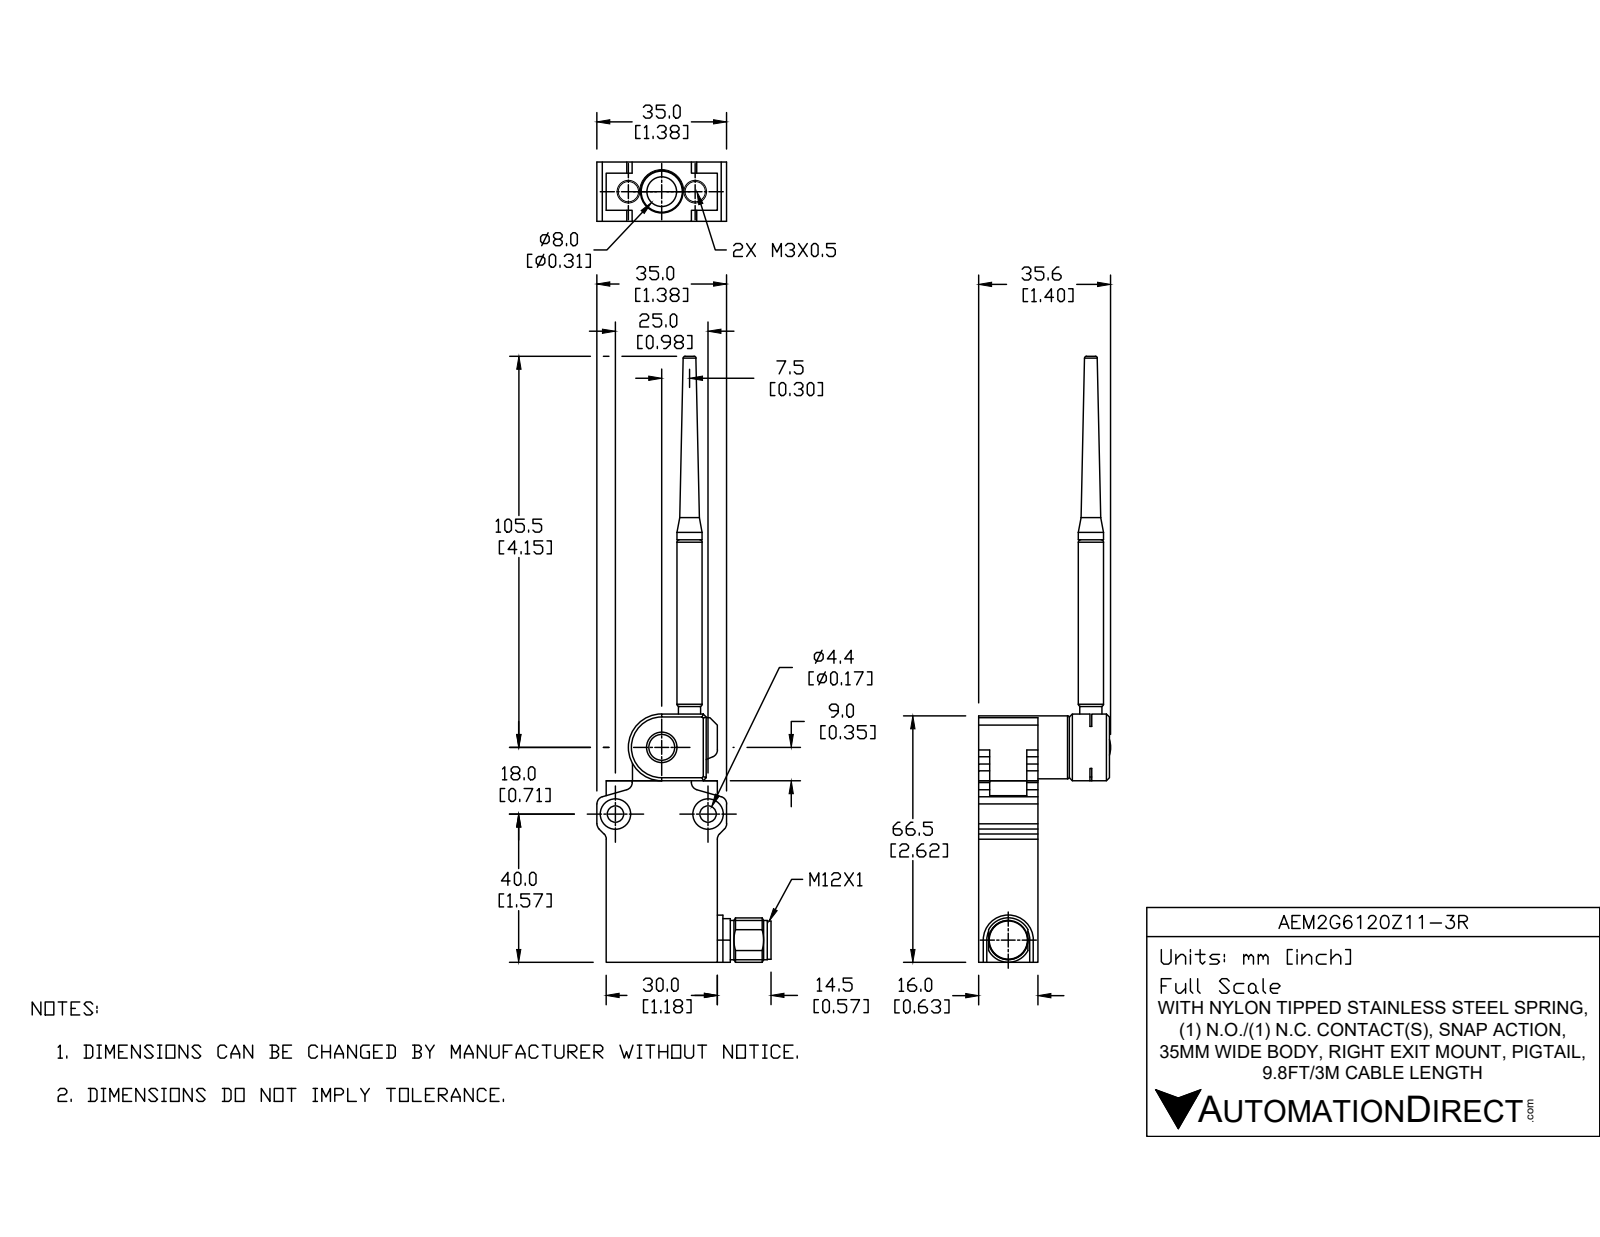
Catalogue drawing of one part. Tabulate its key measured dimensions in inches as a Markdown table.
| quantity | value |
| --- | --- |
| part name | AEM2G6120Z11MR |
| STEP written by | SolidWorks 2019 (AUTOMOTIVE_DESIGN) |
| units | inches |
| bodies | 9 solids, 257 faces (102 planar, 54 cylindrical, 101 other) |
| overall size | 6.476 × 1.831 × 1.374 |
| volume | 2.201 in³ |
| surface area | 22.69 in² |
| round holes (diameter × count) | 0.118 × 2, 0.173 × 2, 0.323 × 2, 0.197 × 1, 0.236 × 1, 0.315 × 1 |
| round bosses / shafts (diameter × count) | 0.622 × 1, 0.472 × 1, 0.417 × 1, 0.406 × 1, 0.276 × 1, 0.268 × 1, 0.138 × 1 |
| partial cylindrical surfaces (radius × count) | 0.079 × 8, 0.256 × 1, 0.354 × 1 |
| main face-to-face distances | 0.63, 1.181, 0.177, 2.047, 0.354, 0.535, 1.165, 0.358, 0.28, 0.902 |
| hole center spacings | 0.863, 0.748, 0.857, 0.984, 1.065 |
